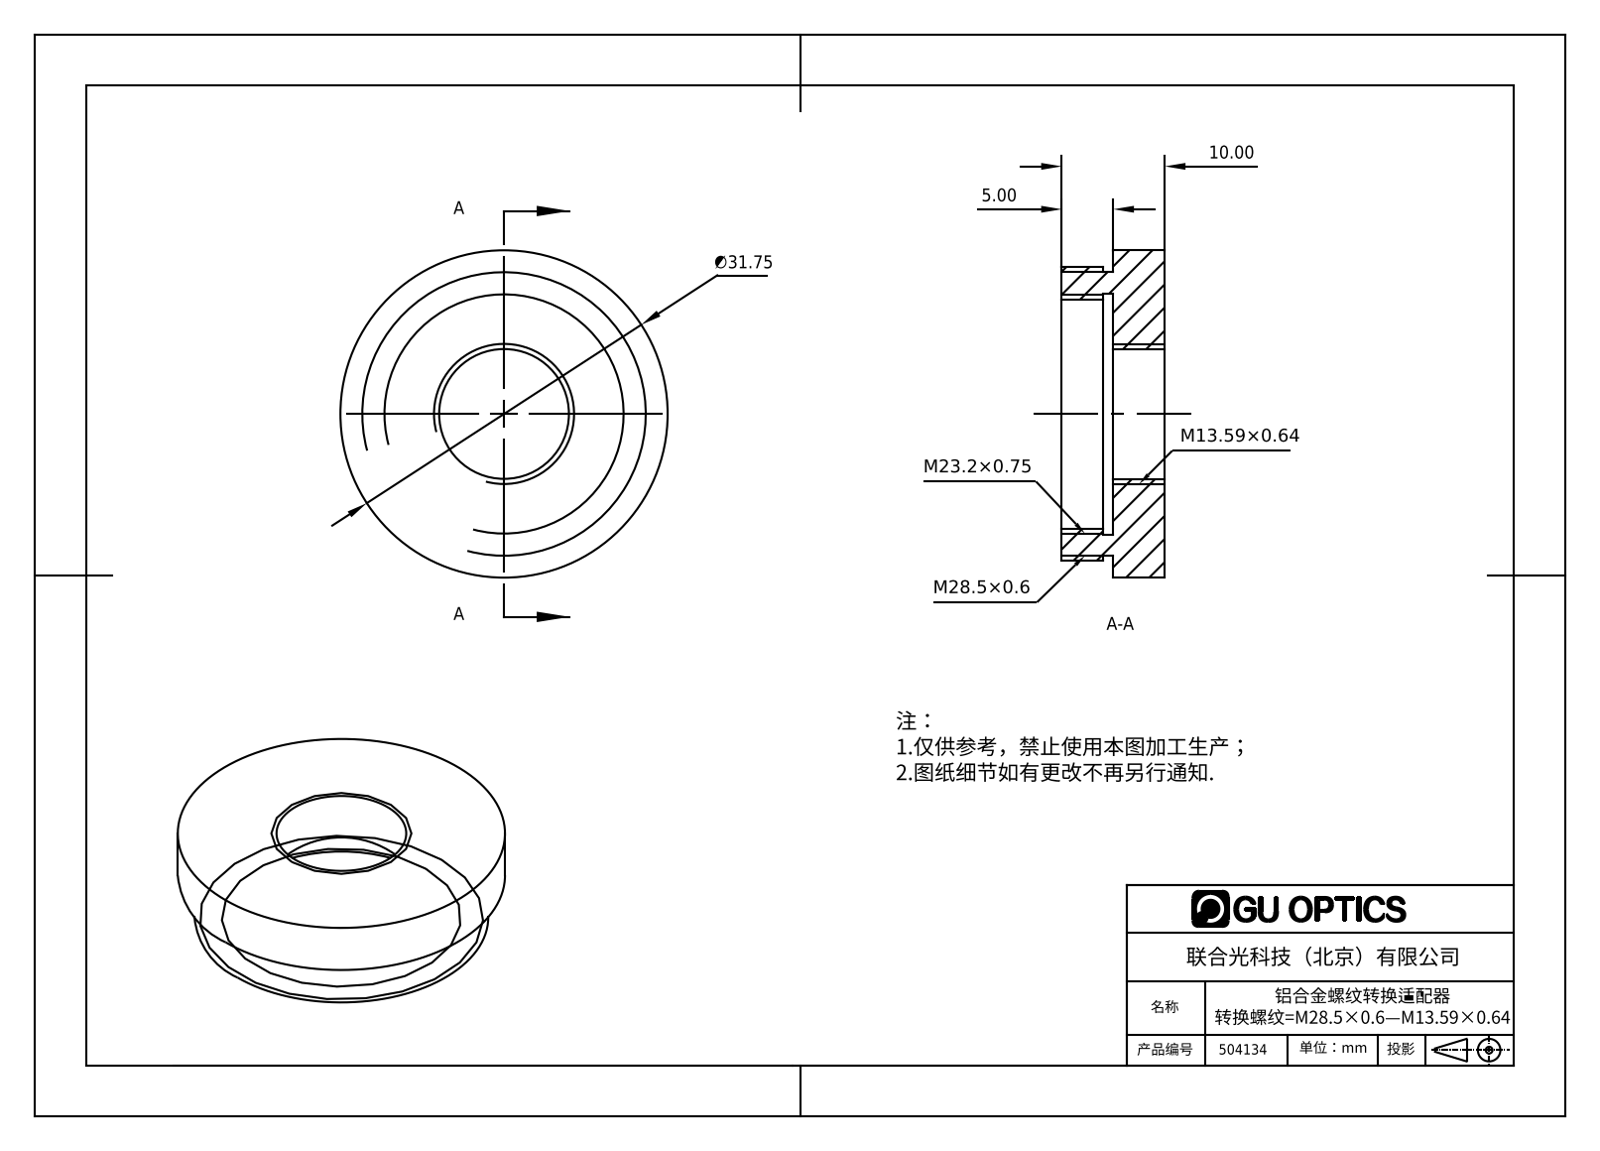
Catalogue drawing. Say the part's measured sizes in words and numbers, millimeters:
The part is named "504134". Its 3-D file was written by "SolidWorks 2016 (AUTOMOTIVE_DESIGN)". It is 1 solid with 18 faces: 6 planar, 12 cylindrical and 0 other. Overall it measures 31.75 by 31.75 by 10 millimeters. Its volume is 4 504 cubic millimeters and its surface area 3 002 square millimeters. Round holes: 1 of diameter 12.59, 1 of diameter 22.2, 1 of diameter 23.4. Round bosses or shafts: 1 of diameter 31.75, 1 of diameter 28.5, 1 of diameter 27.5. The main face-to-face distances are 5, 10, 4, 1, 6.
